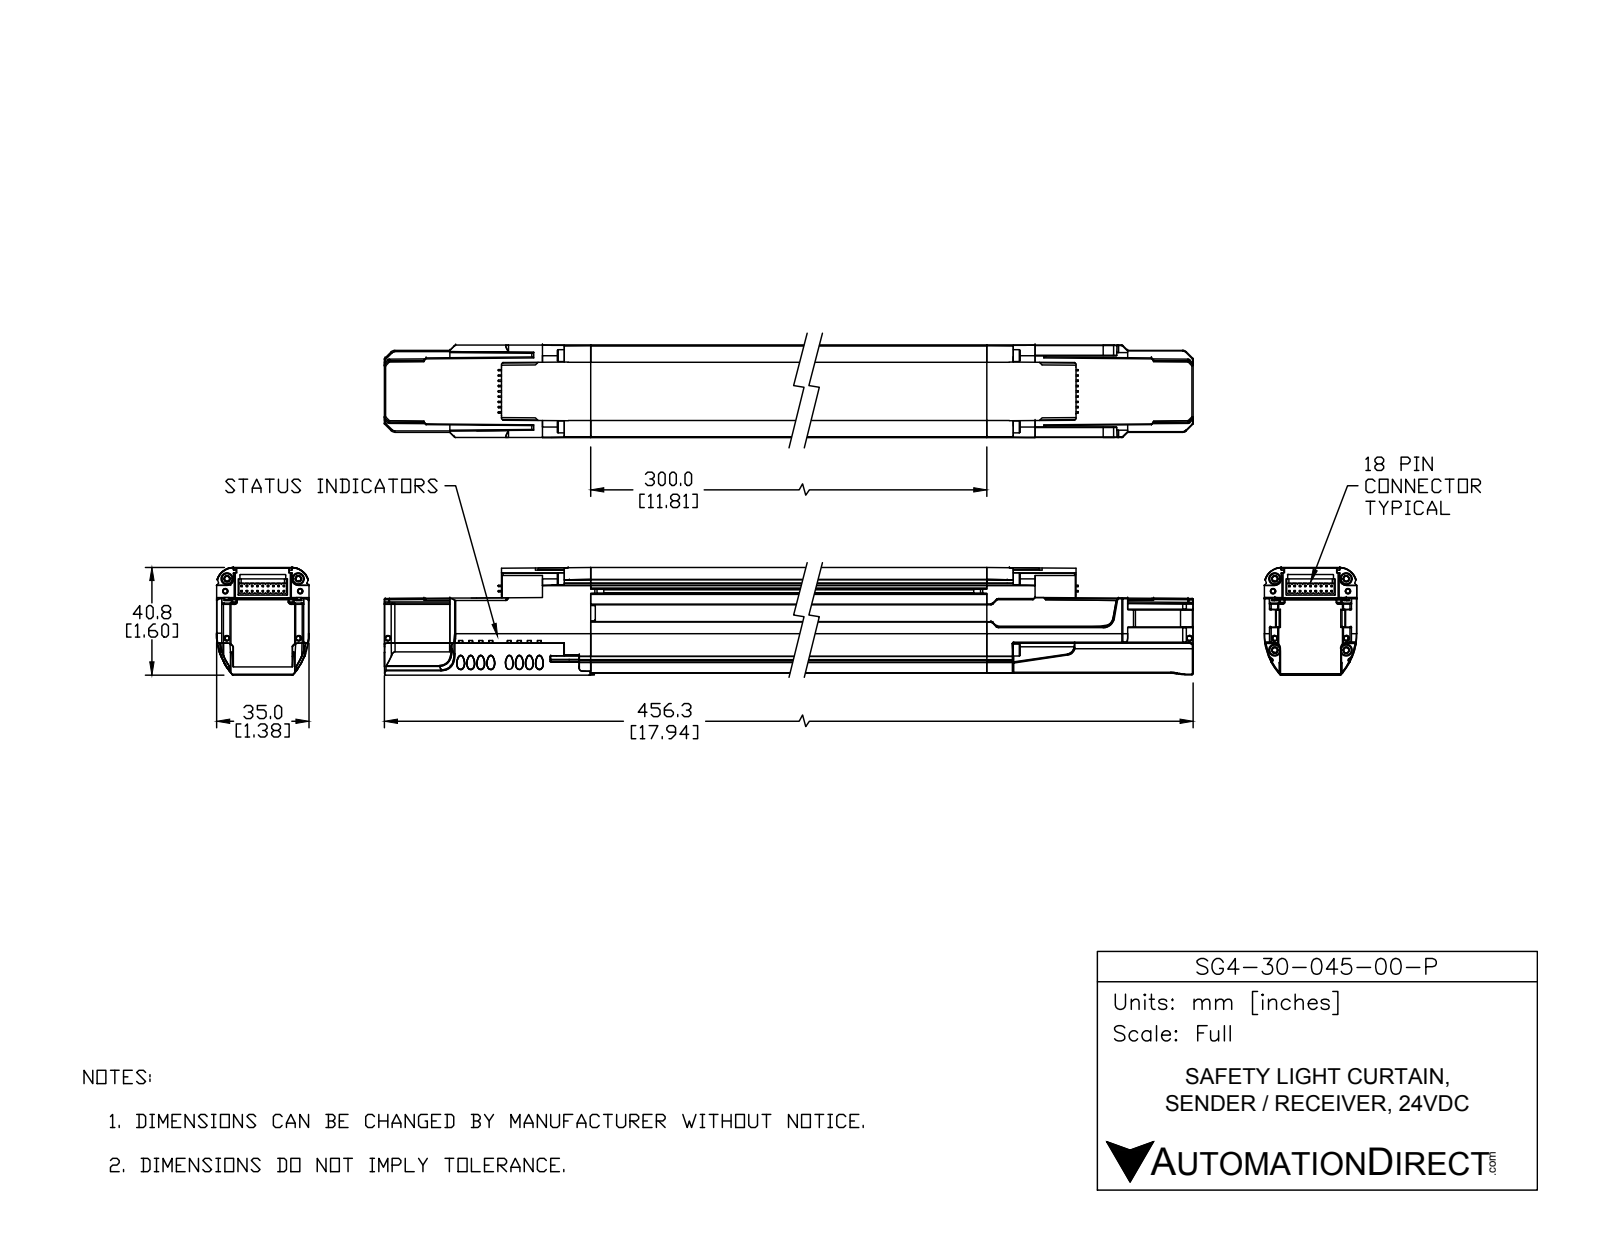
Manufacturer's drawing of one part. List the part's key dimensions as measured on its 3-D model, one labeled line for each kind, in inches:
Part name (STEP PRODUCT): SG4-30-045-OO-P
STEP written by: SolidWorks 2017 (AUTOMOTIVE_DESIGN)
Units: inches
Bodies: 16 solids, 534 faces (362 planar, 110 cylindrical, 62 other)
Overall size (bounding box): 17.963 × 2.58 × 2.023
Volume: 32.97 in³ · Surface area: 199.3 in²
Round holes (diameter × count): ⌀0.07 ×6, ⌀0.1 ×4, ⌀0.165 ×4, ⌀0.209 ×4, ⌀0.26 ×4, ⌀0.065 ×1, ⌀0.065 ×1
Round bosses / shafts (diameter × count): ⌀0.394 ×4, ⌀0.197 ×4
Partial cylindrical surfaces — rounded edges, fillets, slot ends (radius × count): R0.106 ×16, R0.118 ×8, R0.1 ×4, R0.11 ×4, R0.08 ×2, R0.12 ×2, R0.123 ×2, R0.125 ×2
Main face-to-face distances: 0.06, 0.084, 0.024, 1.49, 1.466, 1.55, 1.057, 0.118, 0.481, 0.985
Hole centre spacings: 0.569, 10.235, 0.02, 0.204, 0.207, 0.207, 0.227, 0.71
